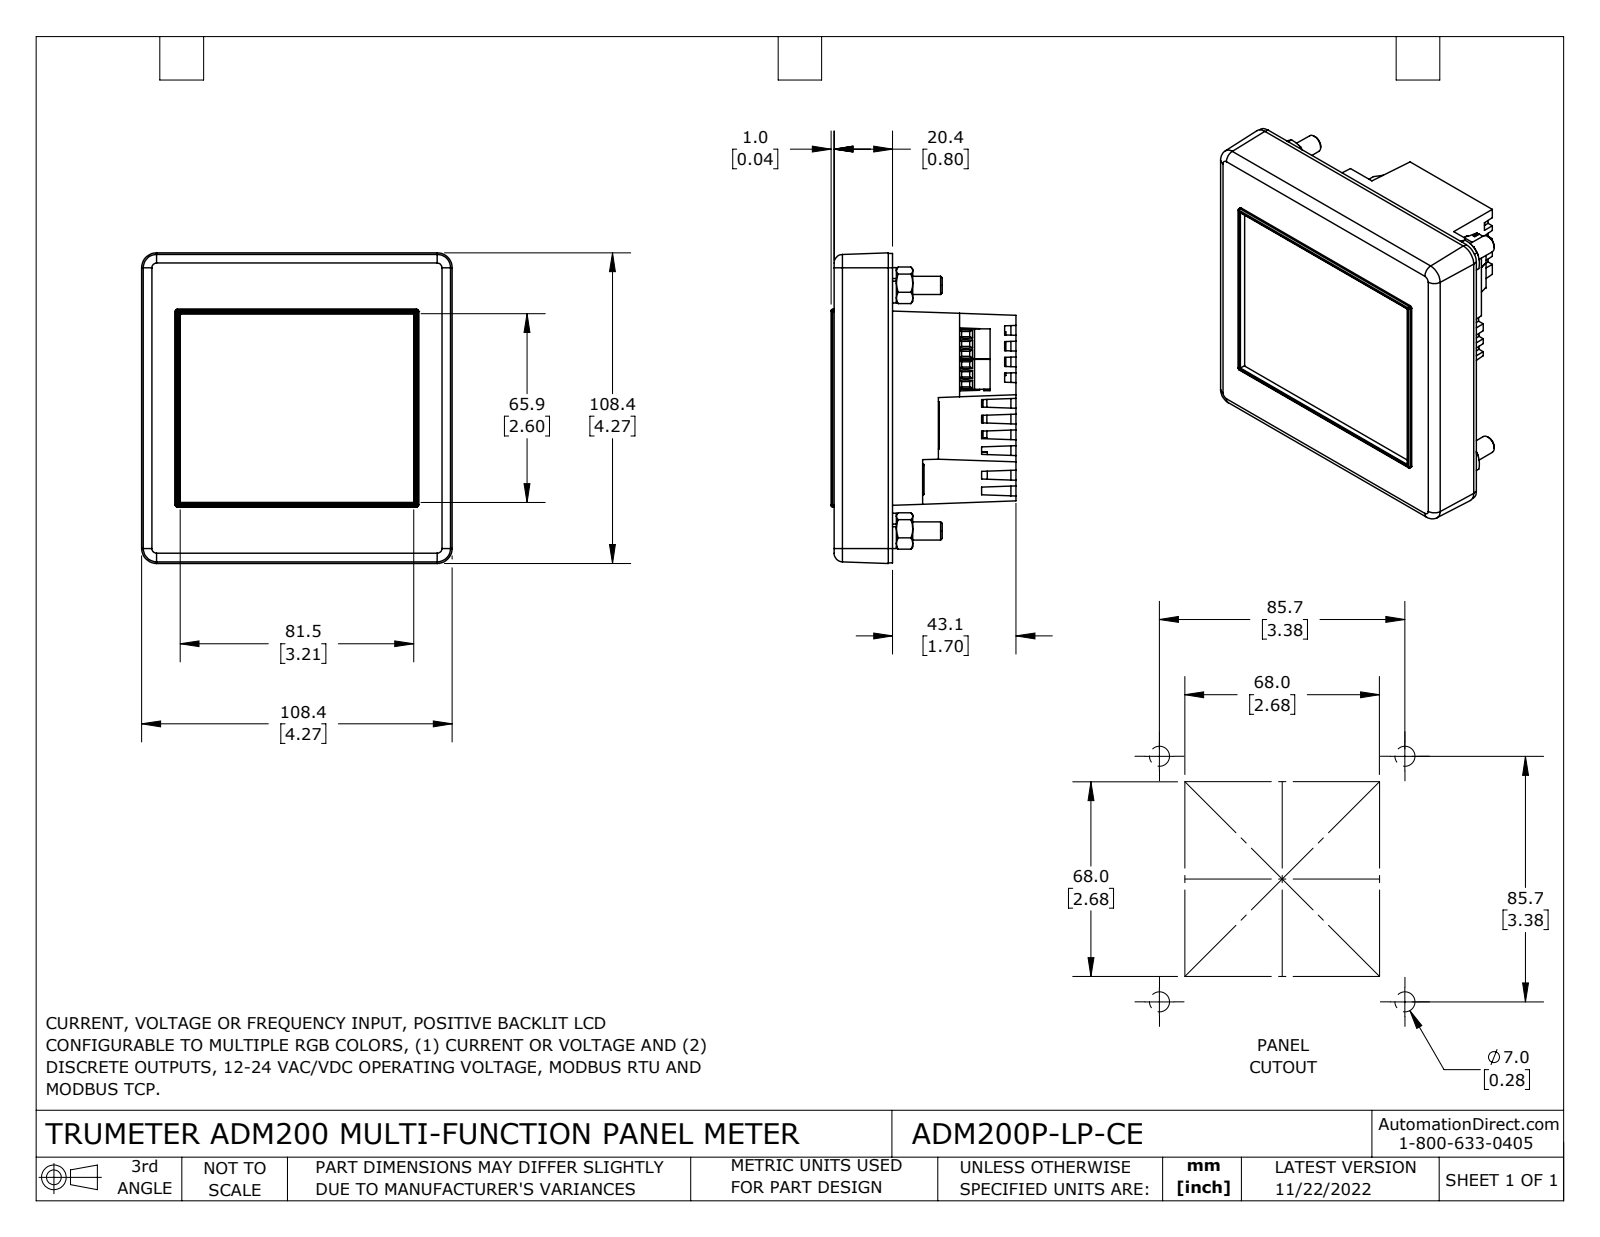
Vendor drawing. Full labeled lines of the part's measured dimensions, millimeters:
Part name (STEP PRODUCT): ADM200P-LP-CE
STEP written by: SolidWorks 2021 (CONFIG_CONTROL_DESIGN)
Units: millimetres
Bodies: 23 solids, 2059 faces (1384 planar, 290 cylindrical, 385 other)
Overall size (bounding box): 108.4 × 108.4 × 64.5
Volume: 128 000 mm³ · Surface area: 123 100 mm²
Round holes (diameter × count): ⌀1.8 ×9, ⌀2.9 ×6, ⌀3 ×5, ⌀5.4 ×4, ⌀6.4 ×4, ⌀6.6 ×4, ⌀7.5 ×4, ⌀3.9 ×2
Round bosses / shafts (diameter × count): ⌀1 ×5, ⌀12.4 ×4, ⌀11.1 ×4, ⌀0.6 ×4, ⌀2 ×2
Partial cylindrical surfaces — rounded edges, fillets, slot ends (radius × count): R0.2 ×32, R0.5 ×30, R1 ×7, R0.4 ×4, R0.8 ×4, R3 ×4, R5 ×4, R0.1 ×2
Main face-to-face distances: 0.8, 16.1, 2.8, 1.9, 1.5, 2, 17.6, 86.2, 88.1, 1.2
Hole centre spacings: 18, 82, 3.5, 7.4, 25, 36, 54, 60.9
